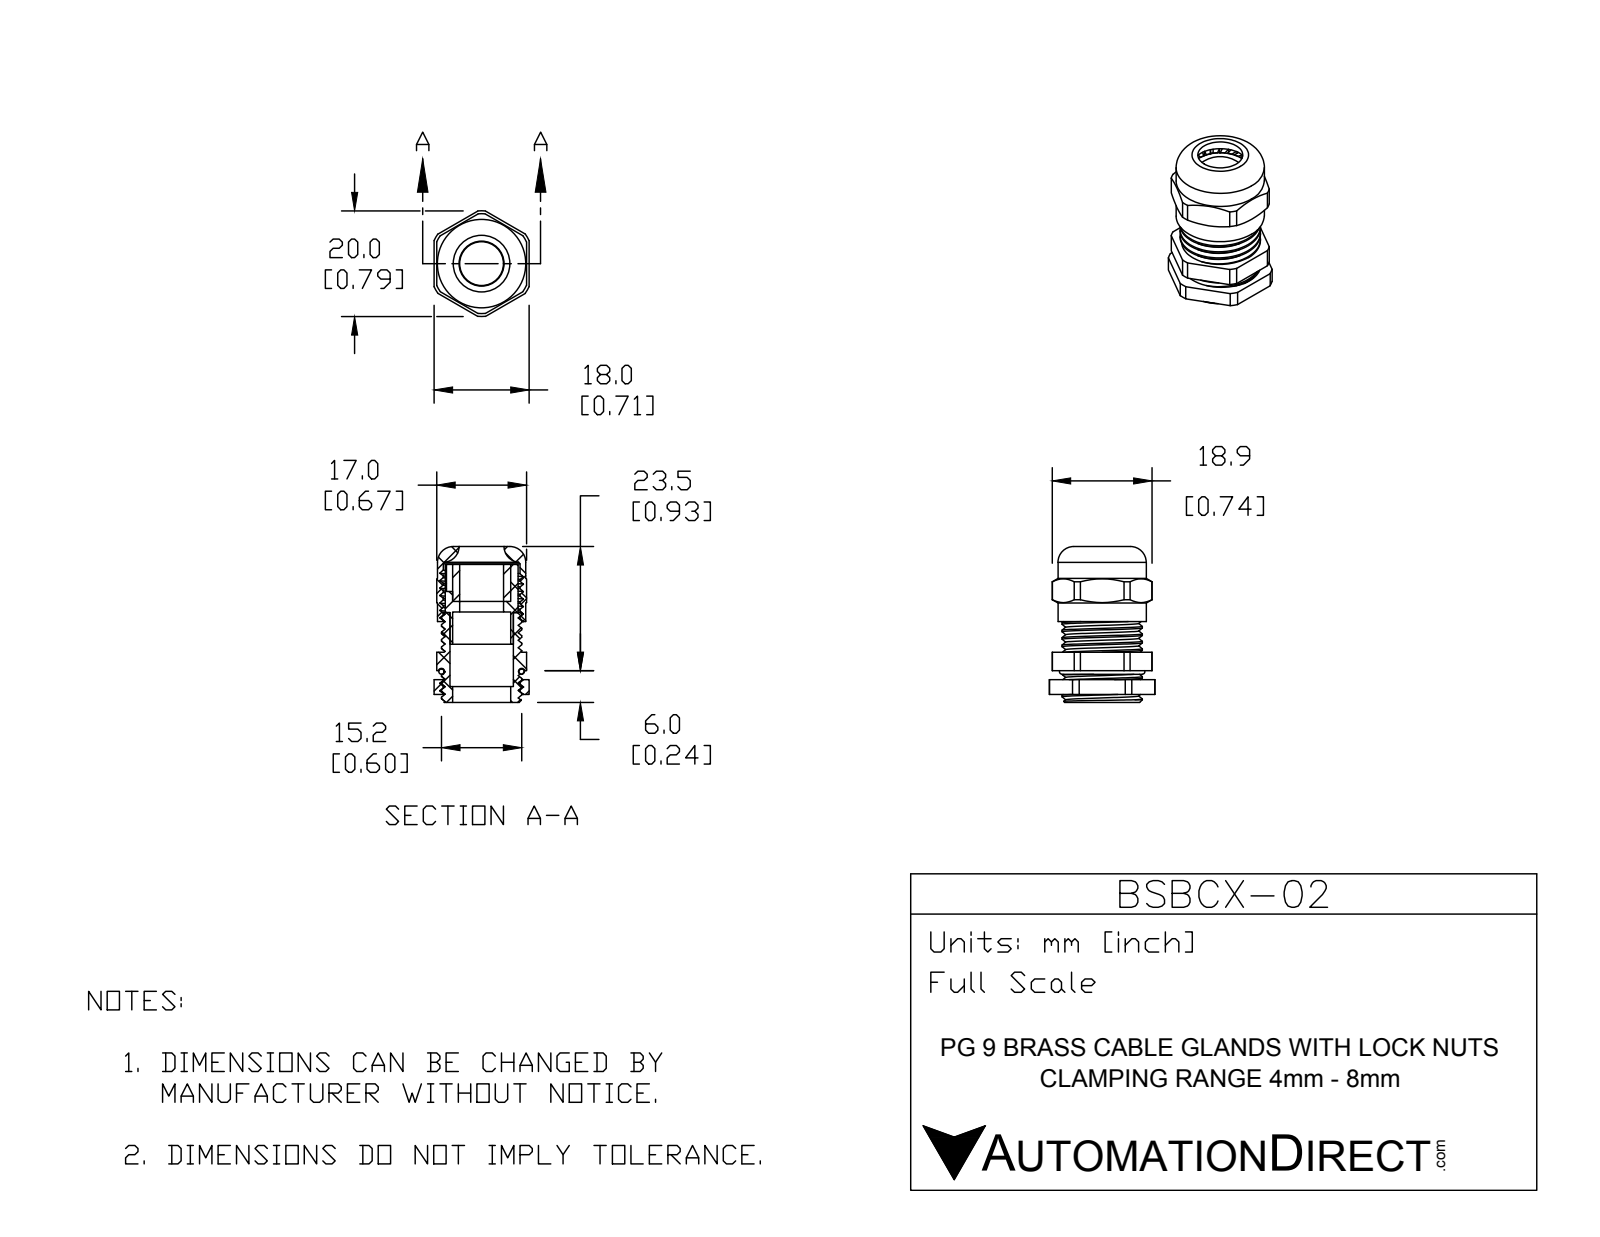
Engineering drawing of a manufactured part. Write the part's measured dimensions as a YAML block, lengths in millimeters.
part_name: "BSBCX-02"
step_written_by: "SolidWorks 2015 (CONFIG_CONTROL_DESIGN)"
units: millimeters
bodies: {solids: 6, faces: 251, planar: 136, cylindrical: 82, other: 33}
overall_size: [29.5, 20, 18]
volume: 3399
surface_area: 6639
round_holes:
  - {diameter: 8.3, count: 1}
  - {diameter: 11, count: 1}
  - {diameter: 12, count: 1}
  - {diameter: 14.53, count: 1}
round_bosses_or_shafts:
  - {diameter: 16.71, count: 1}
  - {diameter: 15.2, count: 1}
  - {diameter: 13.8, count: 1}
partial_cylinders:
  - {radius: 9.45, count: 1}
  - {radius: 10, count: 1}
face_to_face_distances: [0.5, 17, 17.5, 2.8, 11, 1.5, 8, 15.5, 12.7, 18]
